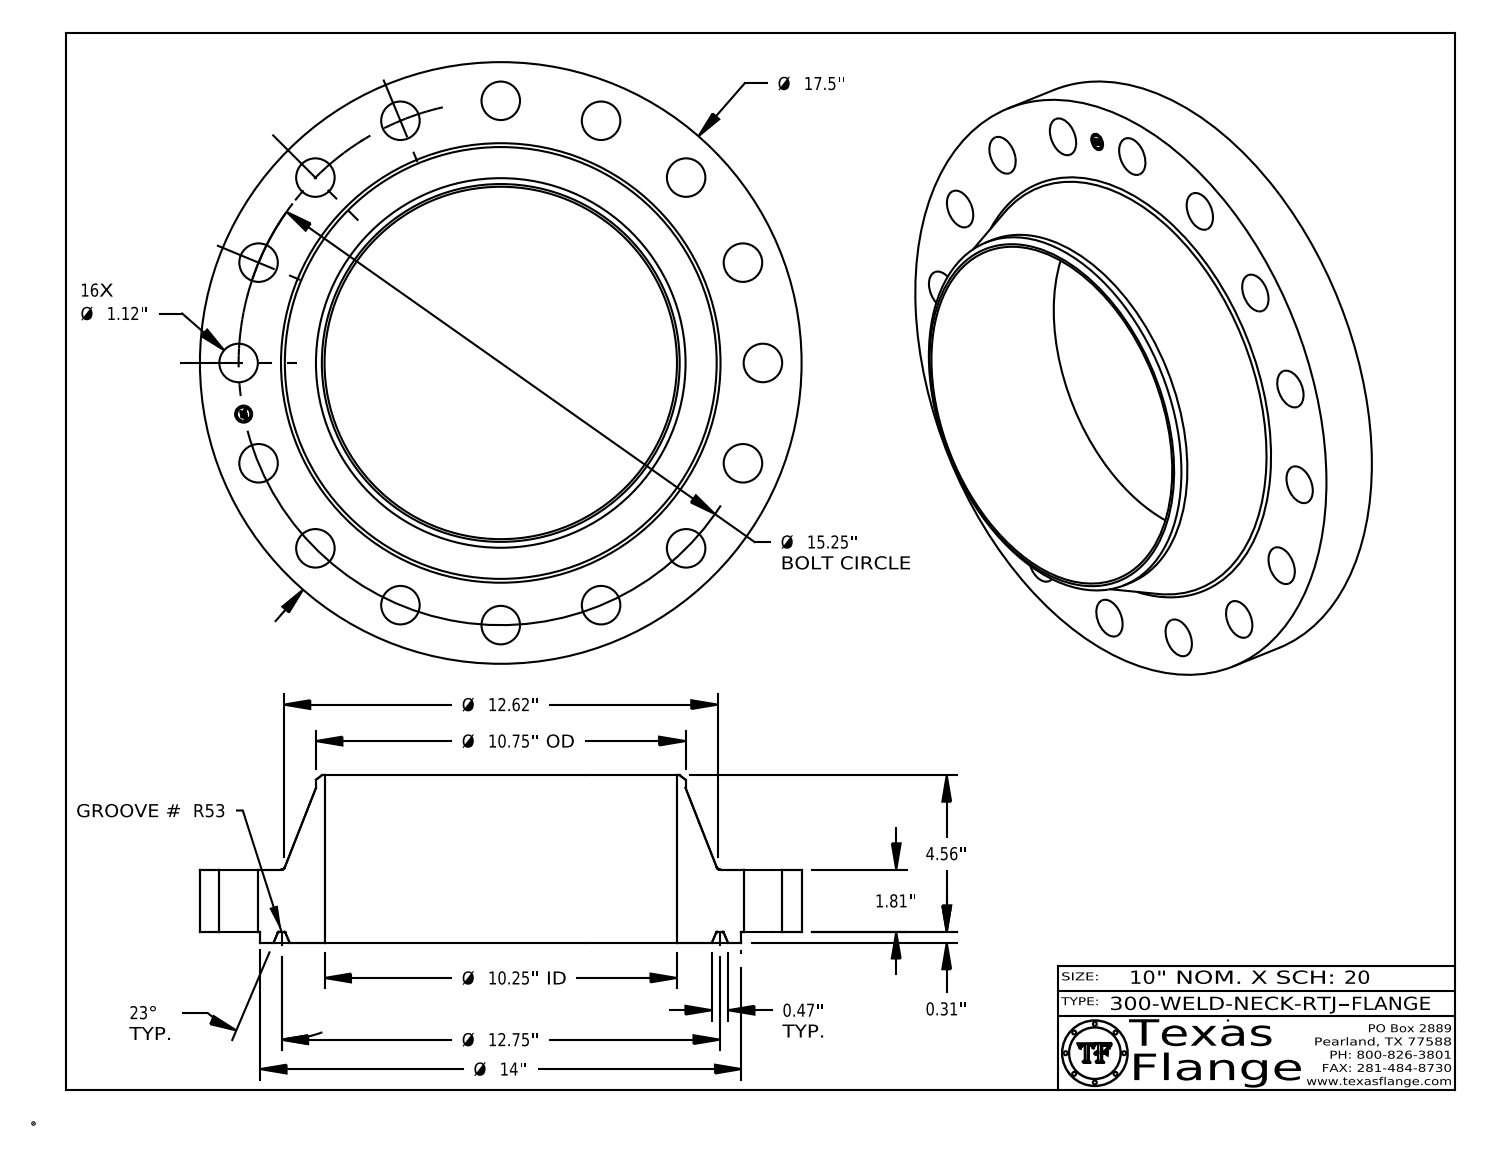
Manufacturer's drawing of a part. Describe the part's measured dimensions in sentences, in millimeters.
The part is named "300-WELD-NECK-RTJ". Its 3-D file was written by "CATIA V5 STEP AP214 (AUTOMOTIVE_DESIGN)". It is 1 solid with 445 faces: 371 planar, 60 cylindrical and 14 other. Overall it measures 444.5 by 444.5 by 123.8 millimeters. Its volume is 5 536 000 cubic millimeters and its surface area 478 200 square millimeters. Round holes: 16 of diameter 28.4, 1 of diameter 12.6, 1 of diameter 260.4. Round bosses or shafts: 8 of diameter 0.8, 1 of diameter 444.5, 1 of diameter 355.6, 1 of diameter 273.1, 1 of diameter 9.9. The main face-to-face distances are 46, 8, 53.9, 123.8, 115.8, 69.9, 0.4, 53.5, 45.6, 70.2. The hole center spacings are 215.2, 273.9, 379.9, 357.9, 193.7, 75.6, 75.6, 148.2.
